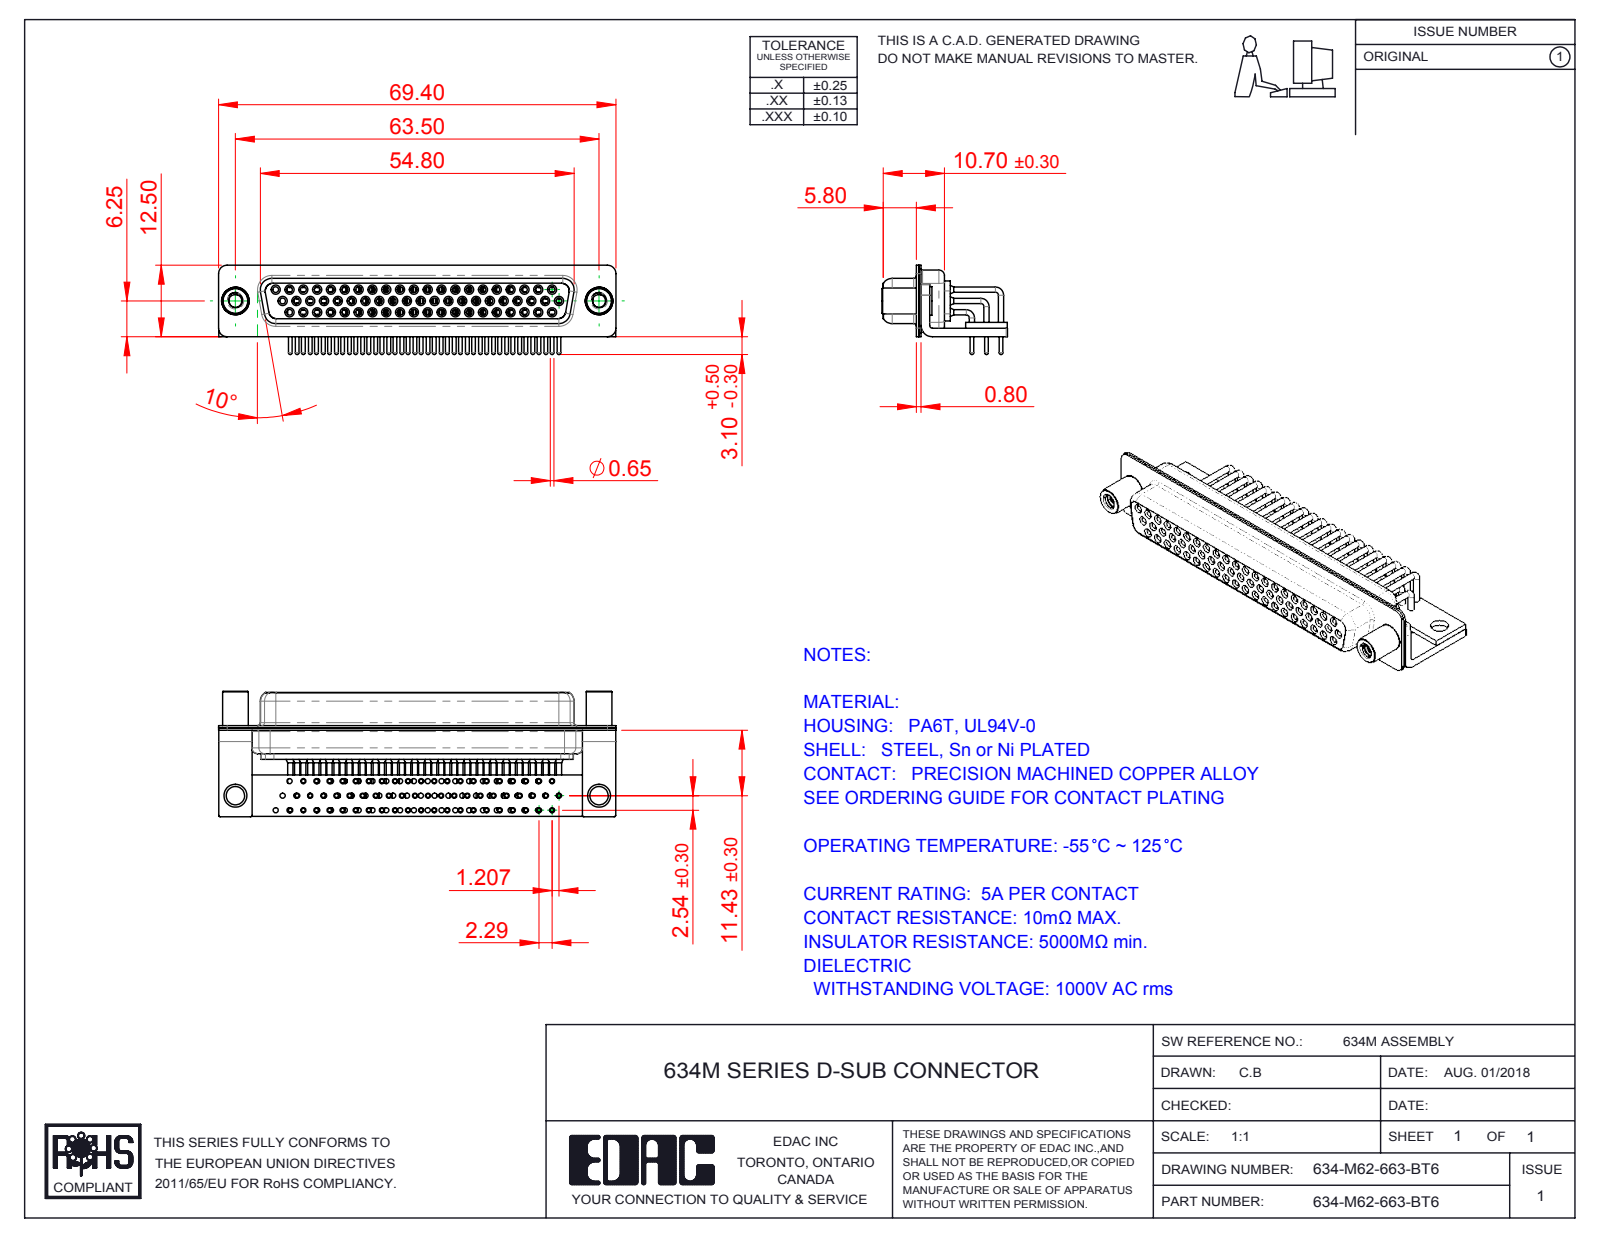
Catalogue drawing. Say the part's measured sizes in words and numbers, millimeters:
The part is named "634M Stabilizer Bracket; 634M 4-40 Threaded Standoff; 634-M62-663-BT6; 634M Shell Front_62 Contacts (+6 more)". Its 3-D file was written by "SolidWorks 2016 (CONFIG_CONTROL_DESIGN)". It is 70 solids with 3789 faces: 1025 planar, 1751 cylindrical and 1013 other. Overall it measures 69.4 by 21.9 by 15.6 millimeters. Its volume is 6 258 cubic millimeters and its surface area 20 041 square millimeters. Round holes: 62 of diameter 0.9, 62 of diameter 1, 62 of diameter 1.1, 62 of diameter 1.7, 62 of diameter 1.8, 62 of diameter 2, 2 of diameter 2.26, 2 of diameter 3.2, 2 of diameter 4, 2 of diameter 4.8. Round bosses or shafts: 118 of diameter 0.9, 62 of diameter 1.6, 62 of diameter 1.5, 62 of diameter 0.65, 56 of diameter 2, 2 of diameter 5, 2 of diameter 4.9, 2 of diameter 4.5. Partial cylindrical surfaces (rounded edges, fillets, slot ends): 16 of radius 0.25, 16 of radius 1.5, 13 of radius 2, 8 of radius 1.35, 8 of radius 1.6, 5 of radius 0.5, 4 of radius 0.6, 4 of radius 0.65. The main face-to-face distances are 0.4, 2.3, 1.9, 1, 8.5, 1.45, 8.95, 0.85, 0.8, 6.2. The hole center spacings are 7.24, 2.41, 9.65, 4.83, 14.48, 16.89, 2.81, 2.32.
